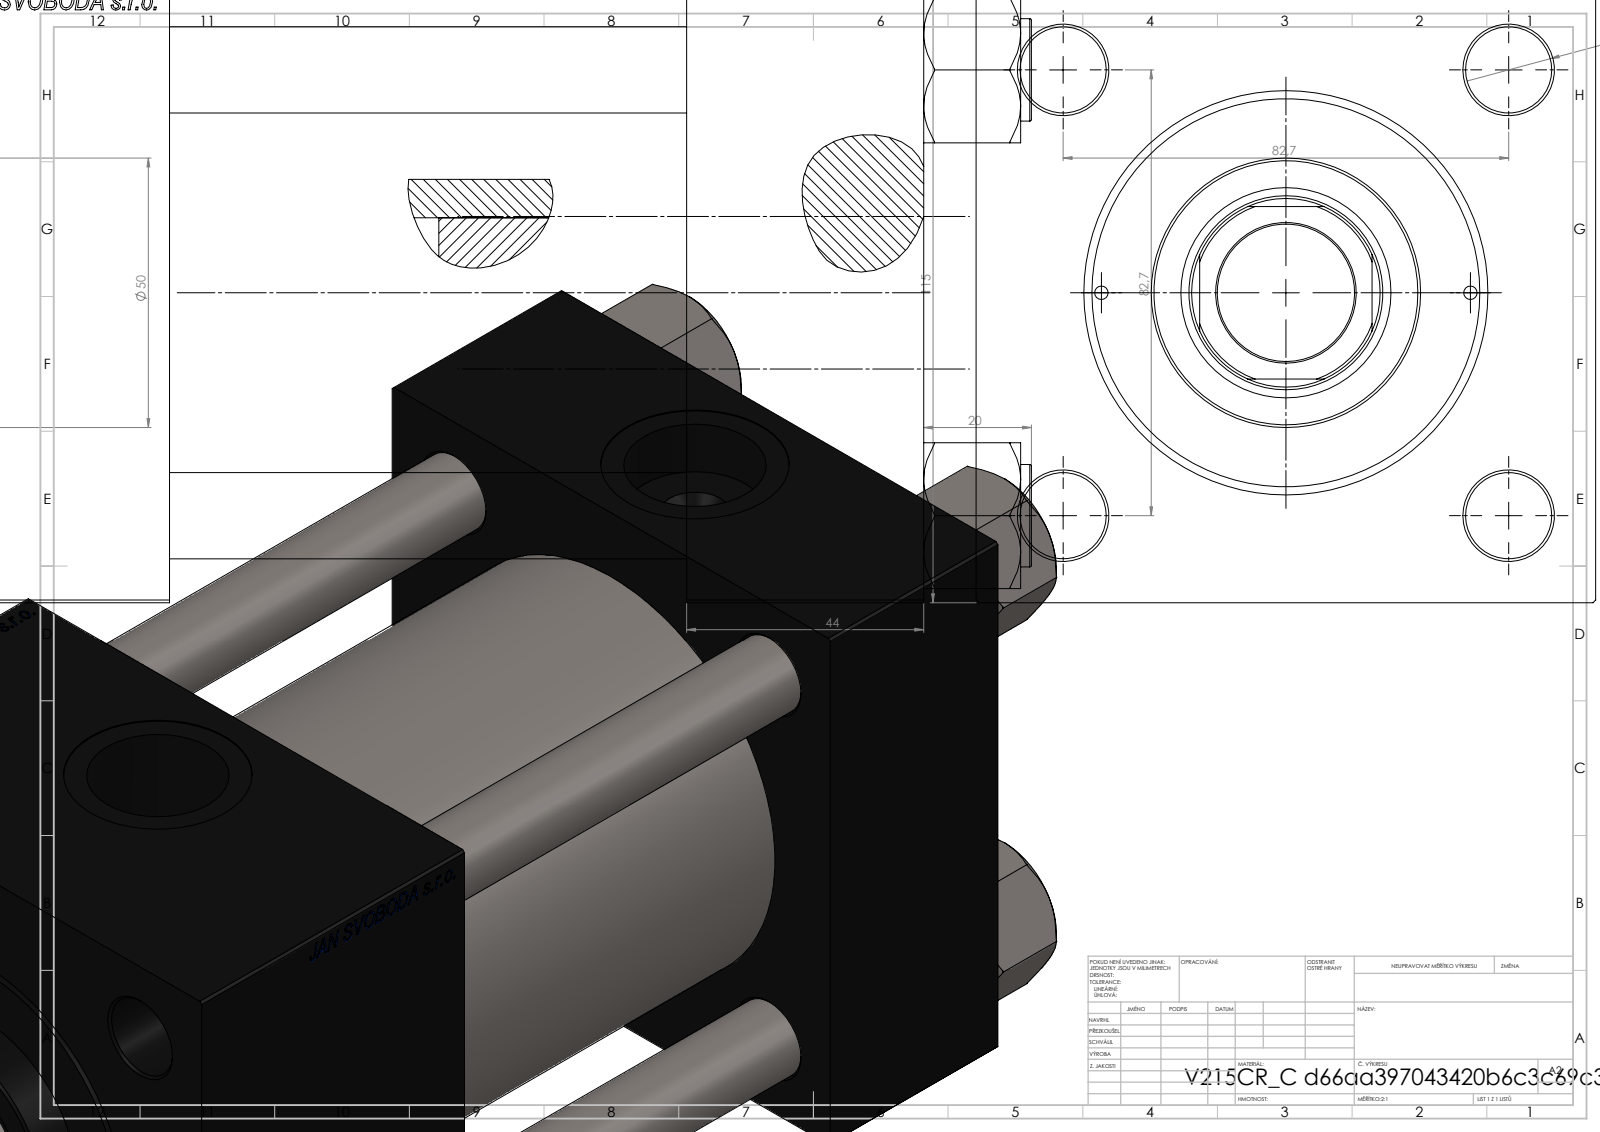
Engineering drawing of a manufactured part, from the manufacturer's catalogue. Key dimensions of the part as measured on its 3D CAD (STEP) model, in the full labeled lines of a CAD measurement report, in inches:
Part name (STEP PRODUCT): V215CR_C_Body; V215CR_VCP_C; V215_VC_A; NUT_M5_C (+1 more)
STEP written by: SolidWorks 2019 (CONFIG_CONTROL_DESIGN)
Units: inches
Bodies: 11 solids, 1203 faces (576 planar, 91 cylindrical, 536 other)
Overall size (bounding box): 10.236 × 4.528 × 4.528
Volume: 113.7 in³ · Surface area: 455.1 in²
Round holes (diameter × count): ⌀0.63 ×4, ⌀0.098 ×2, ⌀0.276 ×2, ⌀1.041 ×2, ⌀1.378 ×2, ⌀1.004 ×1, ⌀1.417 ×1, ⌀1.535 ×1, ⌀2.402 ×1, ⌀2.835 ×1, ⌀3.15 ×1
Round bosses / shafts (diameter × count): ⌀0.748 ×4, ⌀3.386 ×1, ⌀1.969 ×1
Partial cylindrical surfaces — rounded edges, fillets, slot ends (radius × count): R0.689 ×1
Main face-to-face distances: 4.528, 1.732, 8.228, 6.496, 2.717, 5.512, 3.78, 7.098, 5.366, 1.587
Hole centre spacings: 1.652, 2.302, 3.256, 3.393, 1.348, 4.605, 2.697, 5.551
